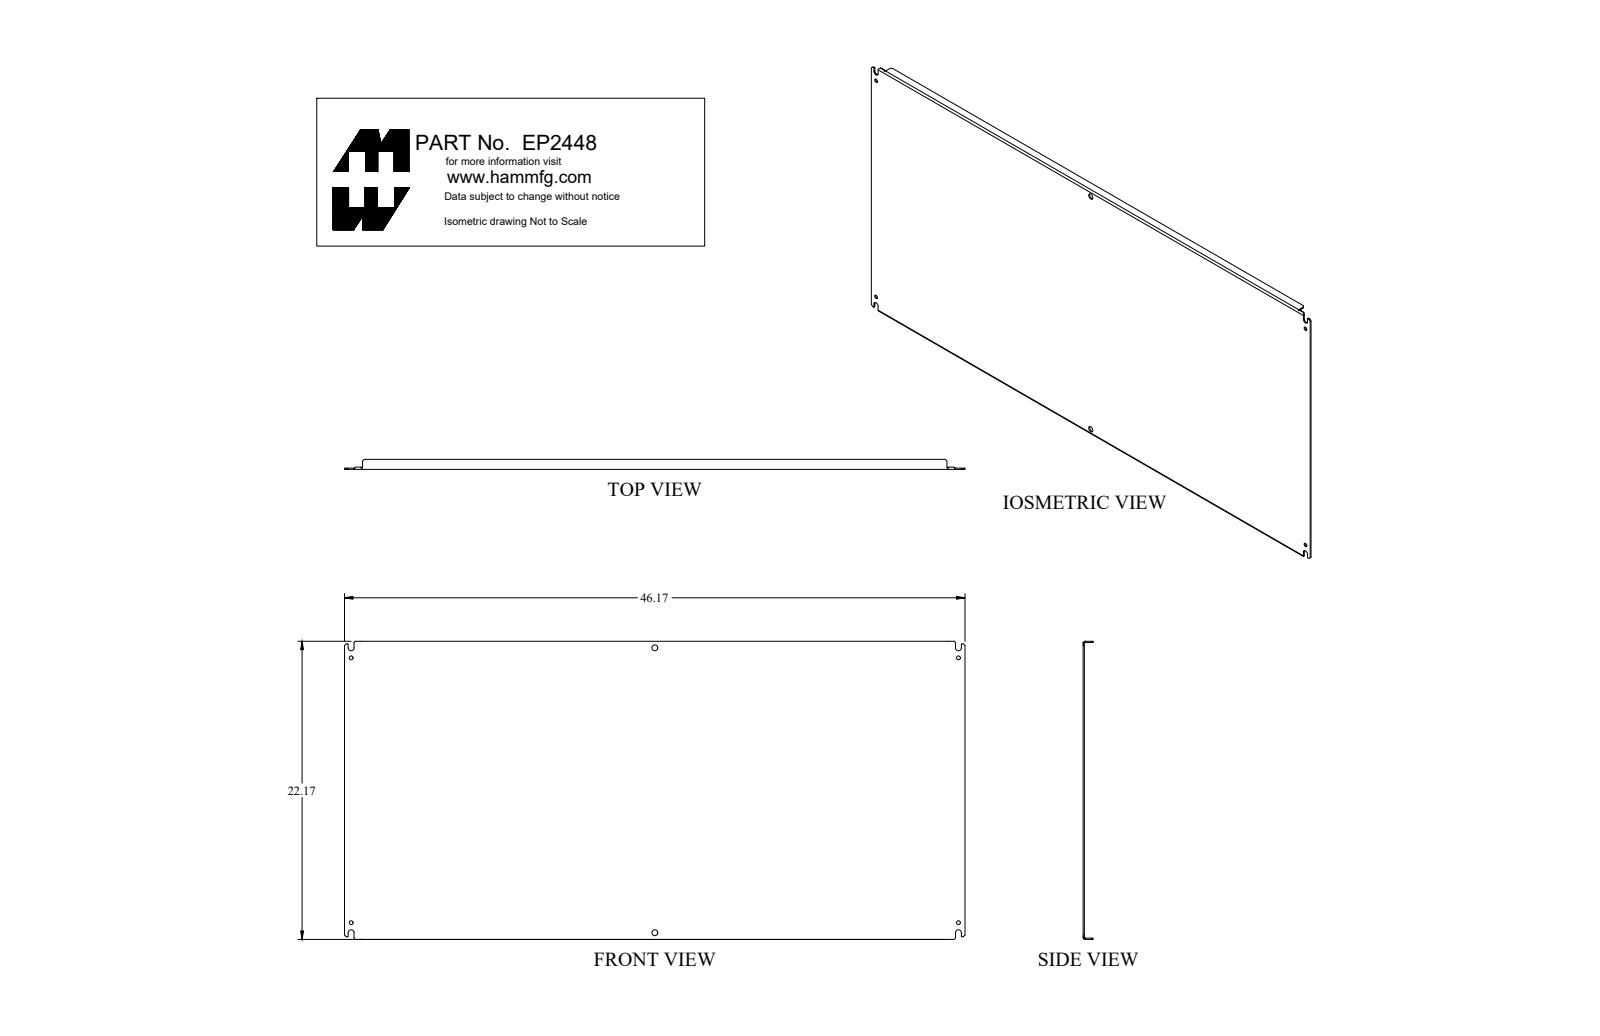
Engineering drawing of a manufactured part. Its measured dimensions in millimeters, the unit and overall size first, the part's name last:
Units: millimetres
Overall size (bounding box): 1172.7 × 563.1 × 19.1
Round holes (diameter × count): ⌀7.1 ×4, ⌀11.1 ×2
Partial cylindrical surfaces — rounded edges, fillets, slot ends (radius × count): R5.6 ×4, R1.2 ×2, R1.6 ×2, R3.6 ×2
Main face-to-face distances: 2.4, 560.7, 558.3, 563.1, 19.1, 16.6, 1172.7, 34.2, 1138.6, 4.3
Hole centre spacings: 574.2, 773.9, 500.1, 1147.8, 1252, 538.2
Volume: 1 673 000 mm³ · Surface area: 1 396 000 mm²
Bodies: 1 solid, 88 faces (50 planar, 30 cylindrical, 8 other)
Part name (STEP PRODUCT): EP2448
STEP written by: SolidWorks 2018 (AUTOMOTIVE_DESIGN)
